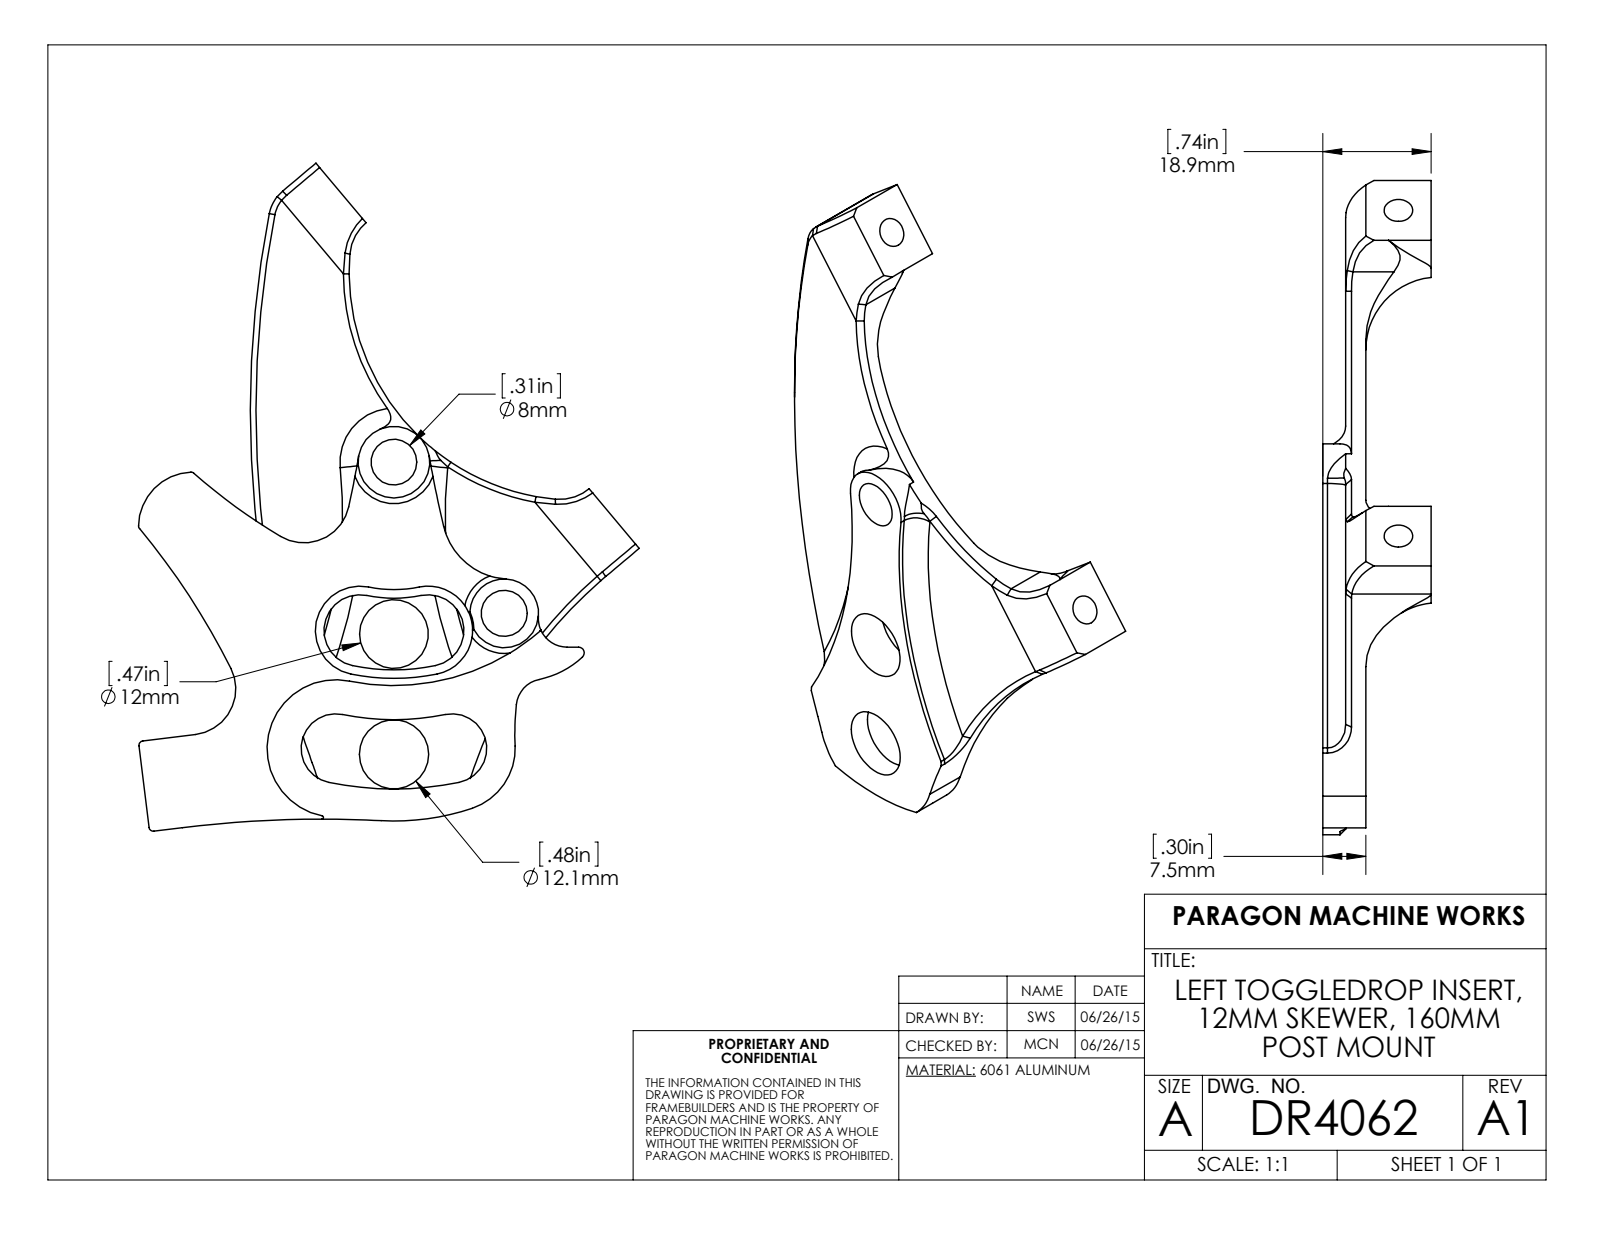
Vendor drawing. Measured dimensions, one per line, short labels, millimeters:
name: DR4062
written by: SolidWorks 2015 (AUTOMOTIVE_DESIGN)
unit: mm
bodies: 1 solid, 79 faces (19 planar, 29 cylindrical, 31 other)
size: 114.19 × 67.9 × 18.9
volume: 19 781 mm³; area: 10 446 mm²
holes: 2× ⌀5, 1× ⌀8.1, 1× ⌀12, 1× ⌀12.1
rounds: 2× R8, 2× R76.25, 1× R6.25, 1× R6.8, 1× R10, 1× R12.7, 1× R14, 1× R39.82
face distances: 3.5, 4, 7.5, 18.9, 14.9, 11.4, 87.81, 13.6, 74.21, 14
hole spacings: 21, 30, 51, 74.2
